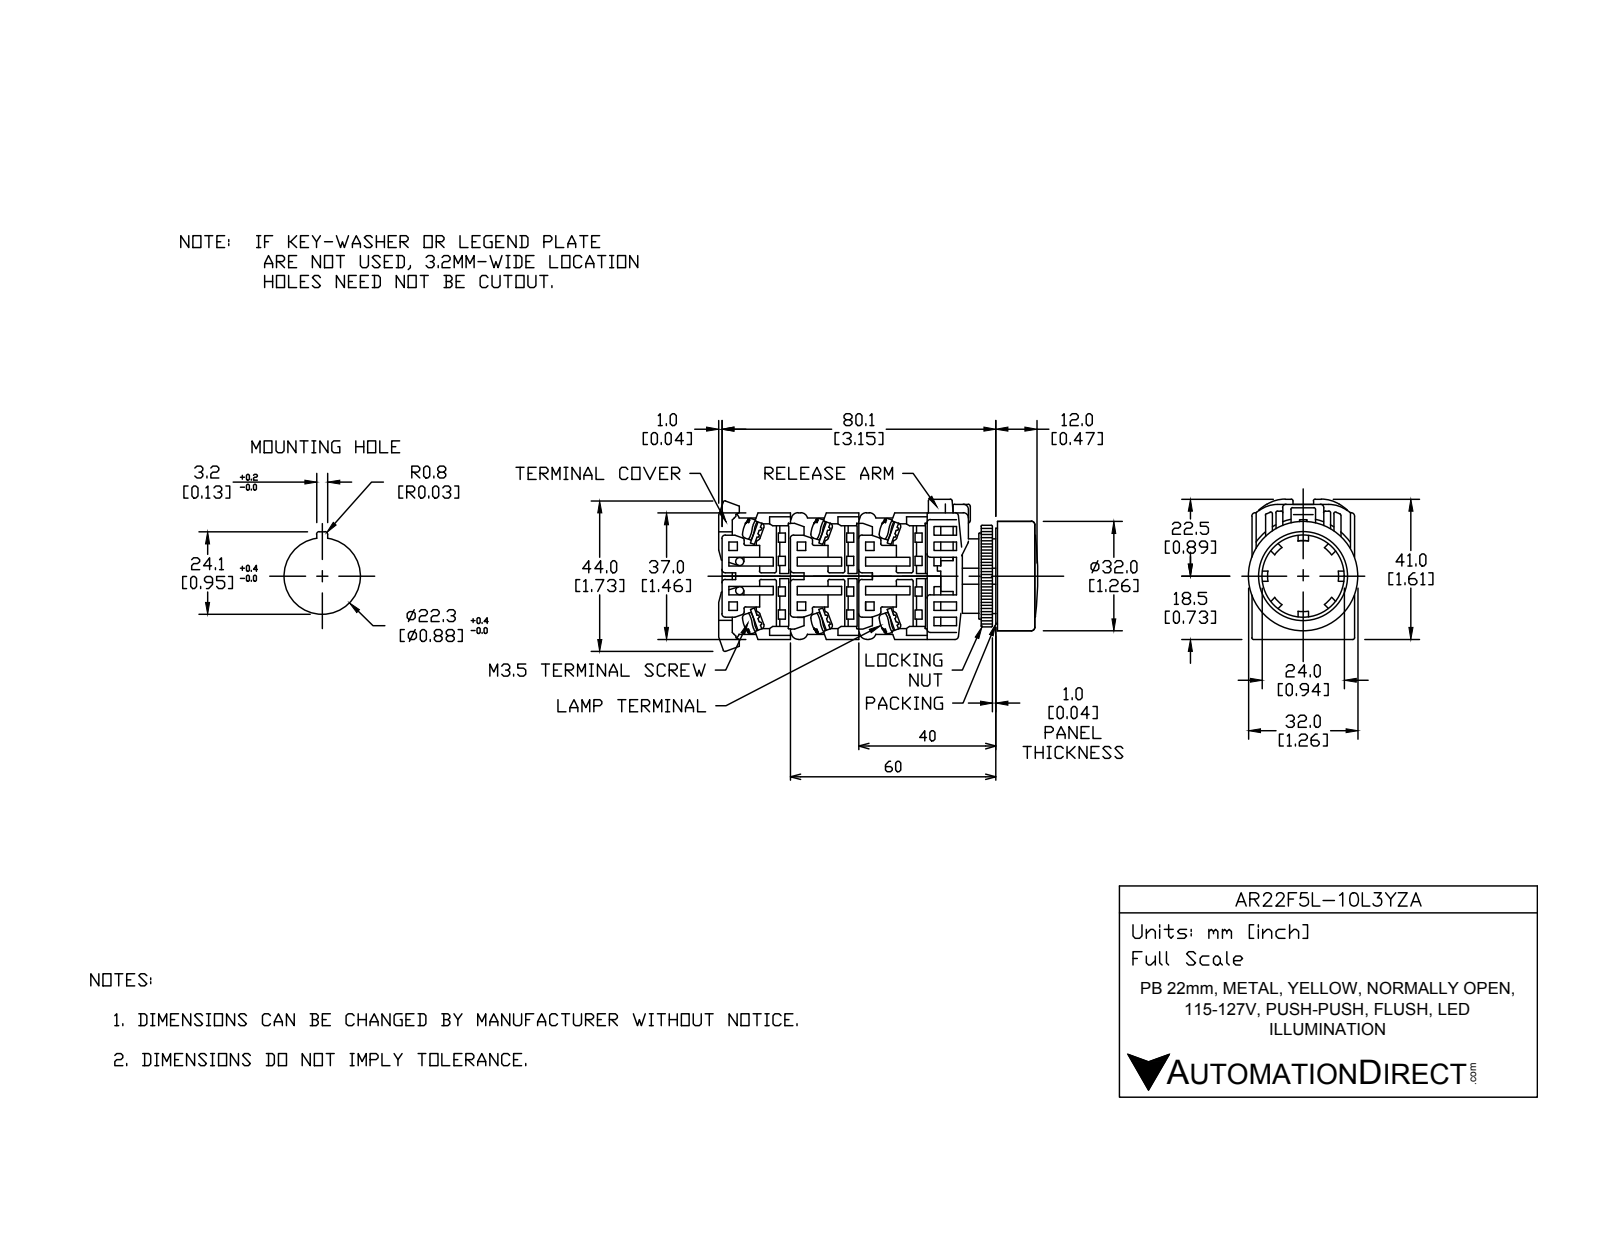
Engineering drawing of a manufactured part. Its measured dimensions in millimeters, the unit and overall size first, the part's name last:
Units: millimetres
Overall size (bounding box): 72.75 × 43.81 × 32
Round holes (diameter × count): ⌀21.8 ×1, ⌀22 ×1, ⌀25 ×1, ⌀31 ×1
Round bosses / shafts (diameter × count): ⌀5 ×4, ⌀32 ×1, ⌀30.5 ×1, ⌀29.8 ×1, ⌀24 ×1, ⌀23.8 ×1, ⌀21.75 ×1, ⌀17 ×1
Partial cylindrical surfaces — rounded edges, fillets, slot ends (radius × count): R0.5 ×32, R1.75 ×8, R5 ×4, R4 ×2, R16.59 ×1, R17.59 ×1
Main face-to-face distances: 1, 18, 29, 20, 28.5, 3, 2, 21, 0.35, 7.5
Volume: 47 521 mm³ · Surface area: 25 721 mm²
Bodies: 16 solids, 451 faces (317 planar, 99 cylindrical, 35 other)
Part name (STEP PRODUCT): AR22F5L-10L3YZA
STEP written by: SolidWorks 2017 (AUTOMOTIVE_DESIGN)
